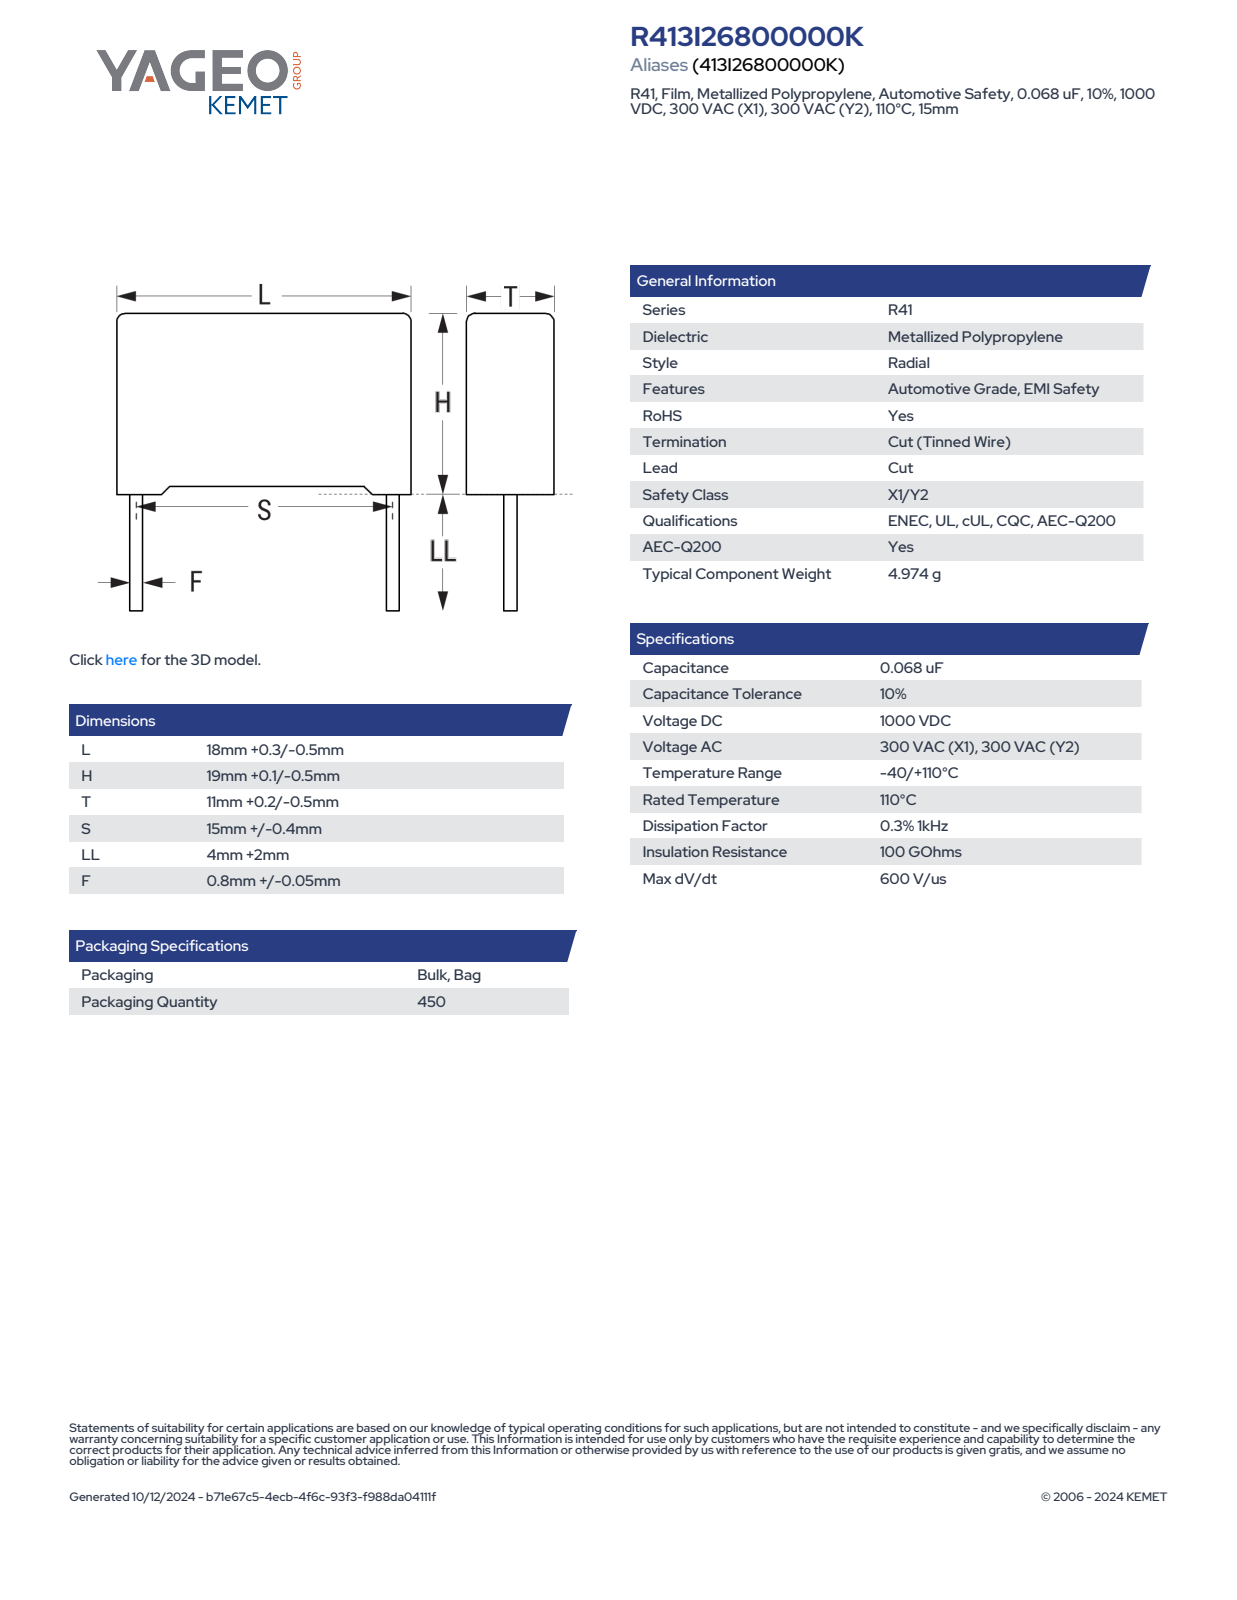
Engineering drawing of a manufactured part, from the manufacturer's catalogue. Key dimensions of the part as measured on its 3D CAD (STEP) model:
Part name (STEP PRODUCT): CFR_RB2_18X19X11_L18.3H19.1T11.2S15LL6F0.85
STEP written by: SolidWorks 2021 (AUTOMOTIVE_DESIGN)
Units: millimetres
Bodies: 4 solids, 85 faces (77 planar, 8 cylindrical, 0 other)
Overall size (bounding box): 25.1 × 18.3 × 11.21
Volume: 3 782 mm³ · Surface area: 1 596 mm²
Round bosses / shafts (diameter × count): ⌀0.85 ×2
Partial cylindrical surfaces — rounded edges, fillets, slot ends (radius × count): R0.5 ×4
Main face-to-face distances: 11.2, 18.3, 18.35, 0.61, 0.75, 19.1, 17.69, 0.66, 18.44, 10.59
